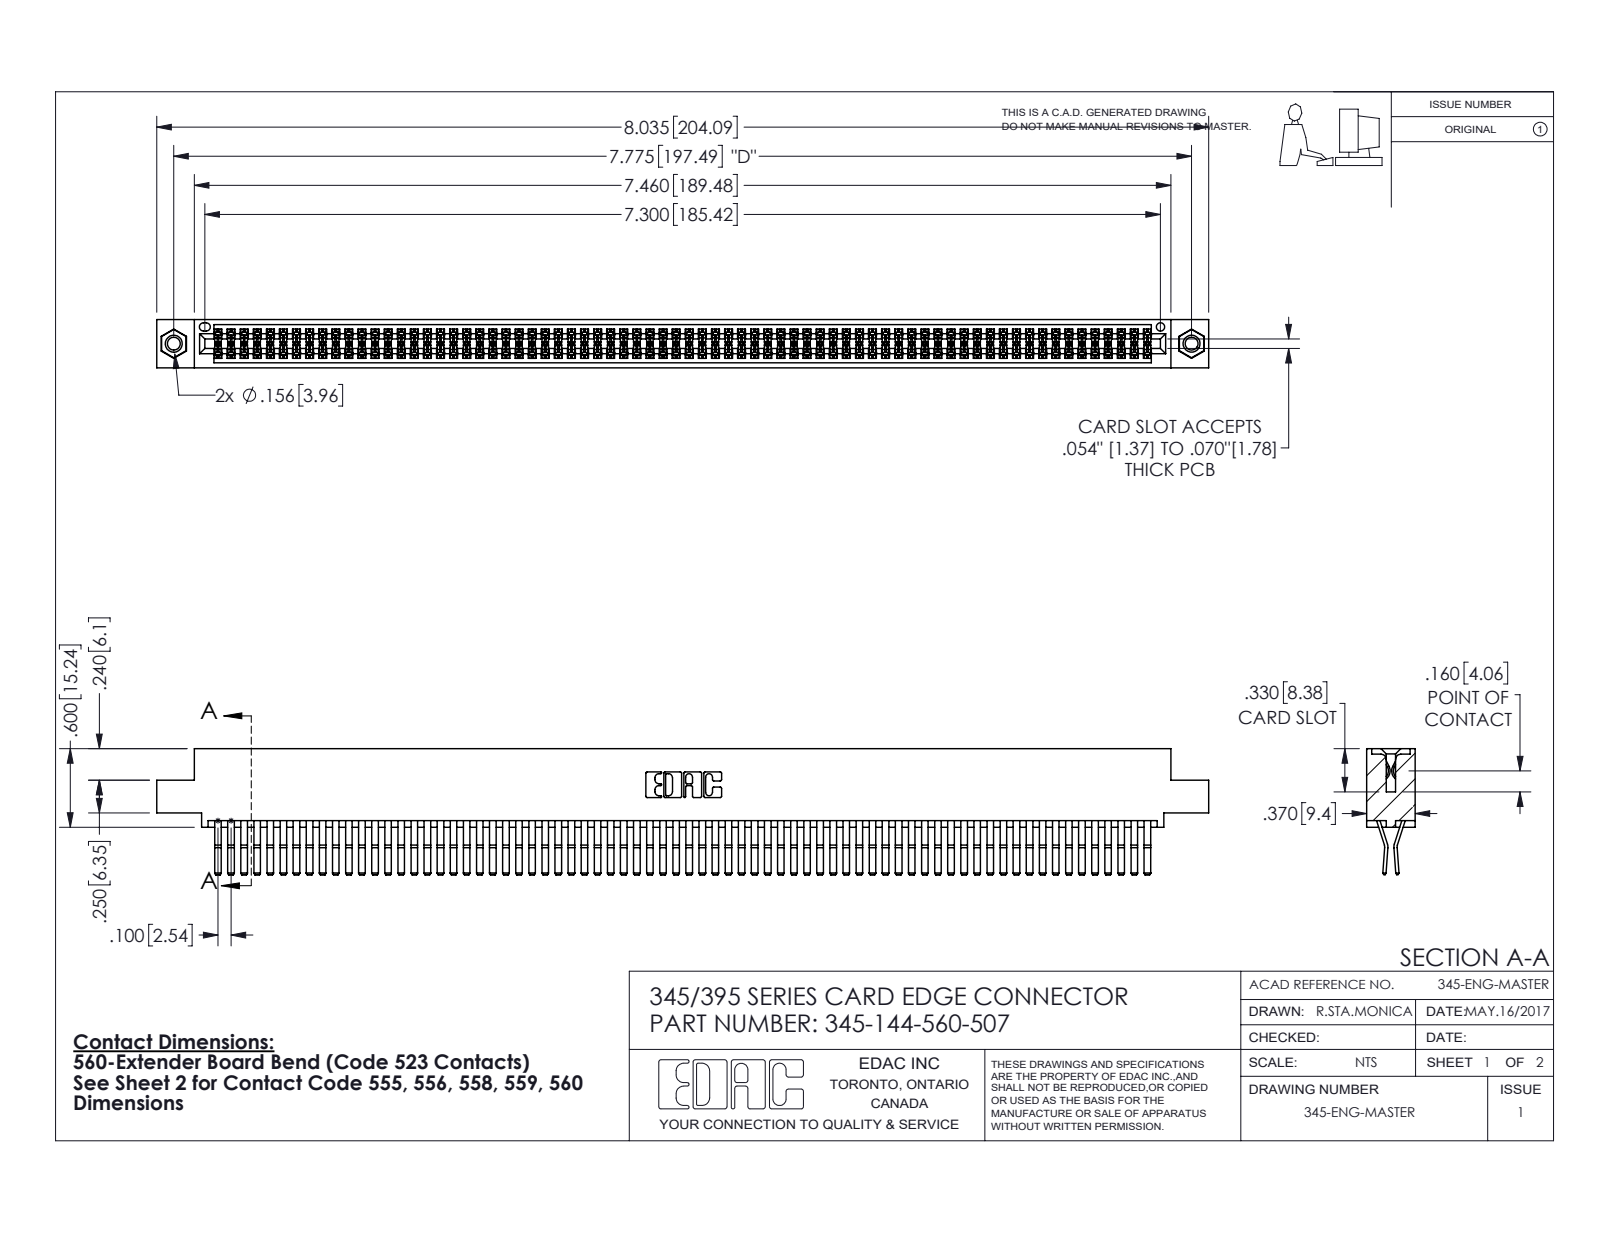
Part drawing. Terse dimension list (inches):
name: 345-144-560-507; 345-250-001_345-250-005-103; 345-292-001_560 Tail; 345 Part_0.110 Offset - 0.156 Dia-TI
written by: SolidWorks 2016 (CONFIG_CONTROL_DESIGN)
unit: in
bodies: 147 solids, 7678 faces (4868 planar, 2794 cylindrical, 16 other)
size: 8.035 × 0.962 × 0.37
volume: 1.279 in³; area: 52.88 in²
holes: 2× ⌀0.098, 2× ⌀0.125, 2× ⌀0.156, 1× ⌀0.064
bosses: 2× ⌀0.155
rounds: 217× R0.006, 22× R0.01, 6× R0.007, 6× R0.031, 3× R0.026, 2× R0.01, 2× R0.014, 2× R0.019
face distances: 0.025, 0.072, 0.298, 0.37, 0.2, 0.098, 0.272, 0.225, 0.175, 0.149
hole spacings: 0.27, 7.539, 7.775
